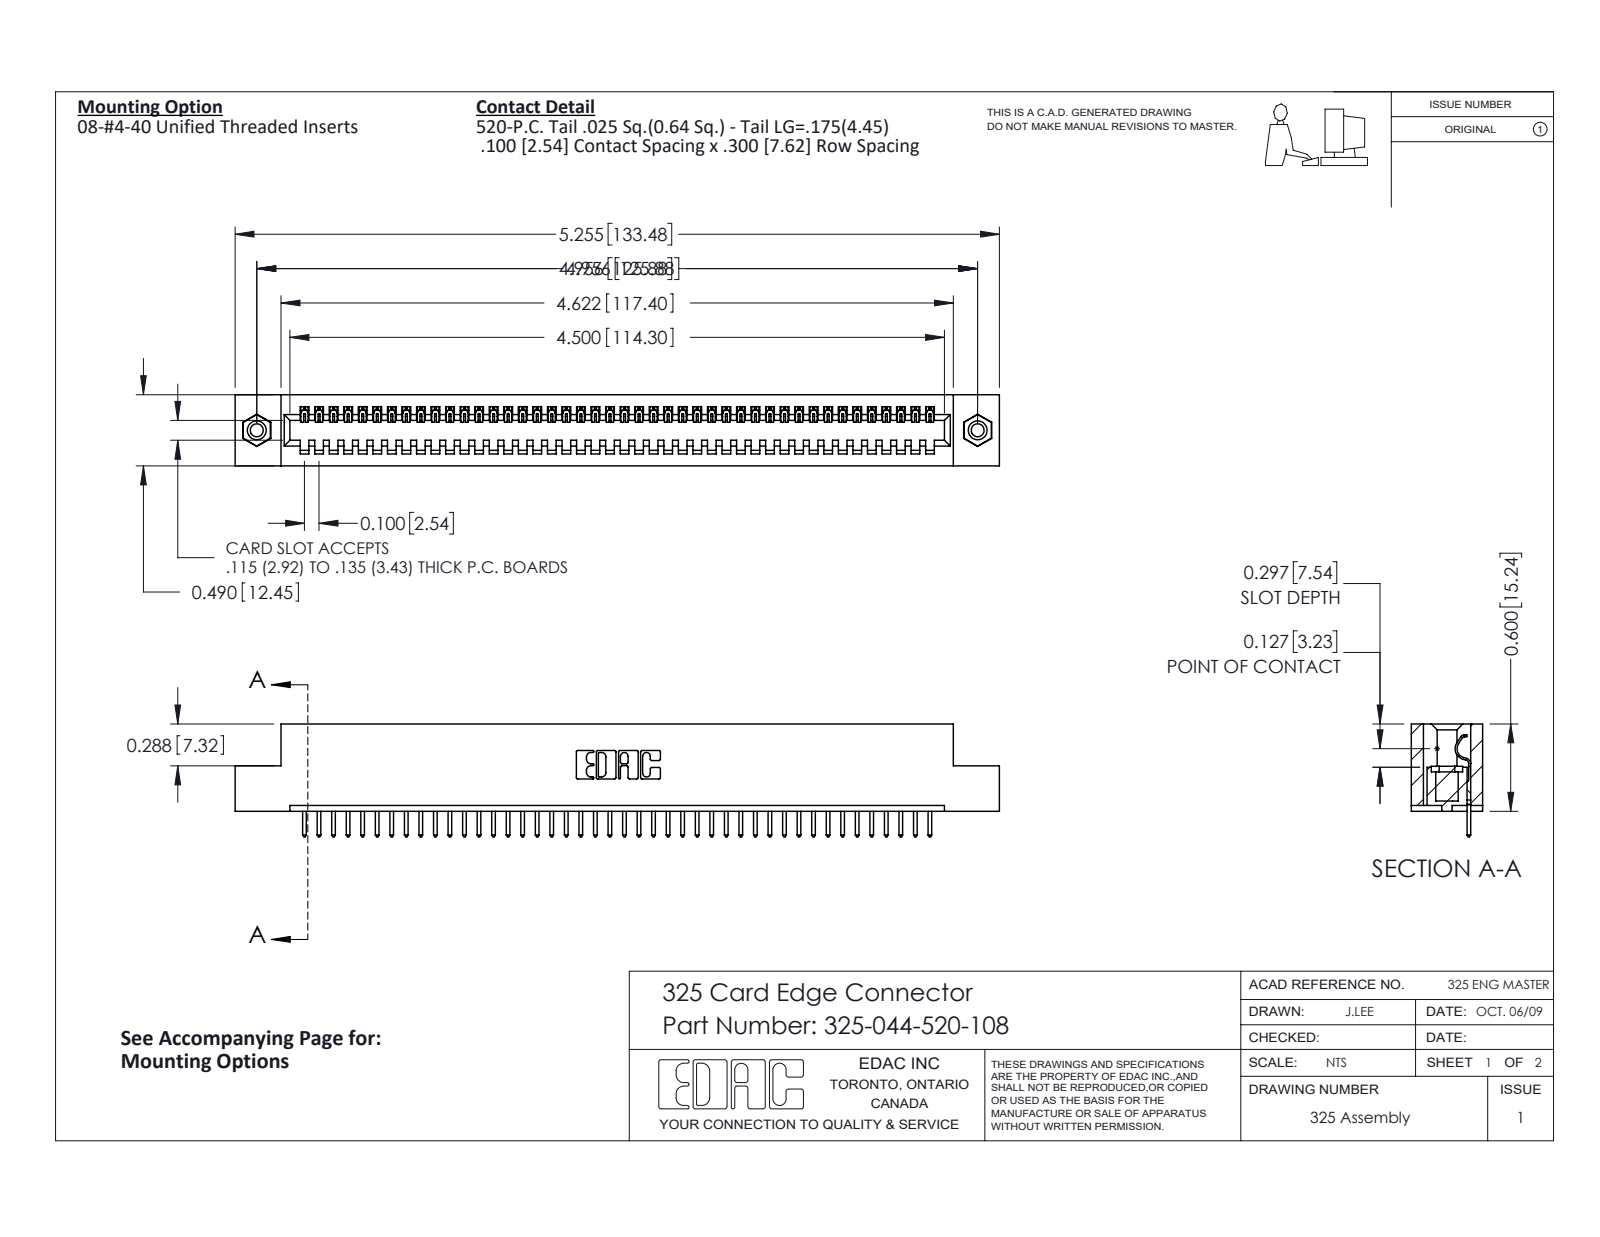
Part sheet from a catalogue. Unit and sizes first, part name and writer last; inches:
Units: inches
Overall size (bounding box): 5.255 × 0.775 × 0.49
Round holes (diameter × count): ⌀0.089 ×2, ⌀0.125 ×2, ⌀0.16 ×2
Round bosses / shafts (diameter × count): ⌀0.155 ×2
Partial cylindrical surfaces — rounded edges, fillets, slot ends (radius × count): R0.006 ×88, R0.01 ×88, R0.01 ×22, R0.007 ×6, R0.031 ×6, R0.026 ×3, R0.014 ×1, R0.022 ×1
Main face-to-face distances: 0.083, 0.407, 0.49, 0.3, 0.107, 0.383, 0.025, 0.325, 0.56, 0.04
Hole centre spacings: 4.956
Volume: 1.028 in³ · Surface area: 27.88 in²
Bodies: 47 solids, 2726 faces (1950 planar, 760 cylindrical, 16 other)
Part name (STEP PRODUCT): 345-250-001_345-250-003-102; 325-292-001_325-293-120; 325-044-520-108; 325 Part_TI
STEP written by: SolidWorks 2016 (CONFIG_CONTROL_DESIGN)
